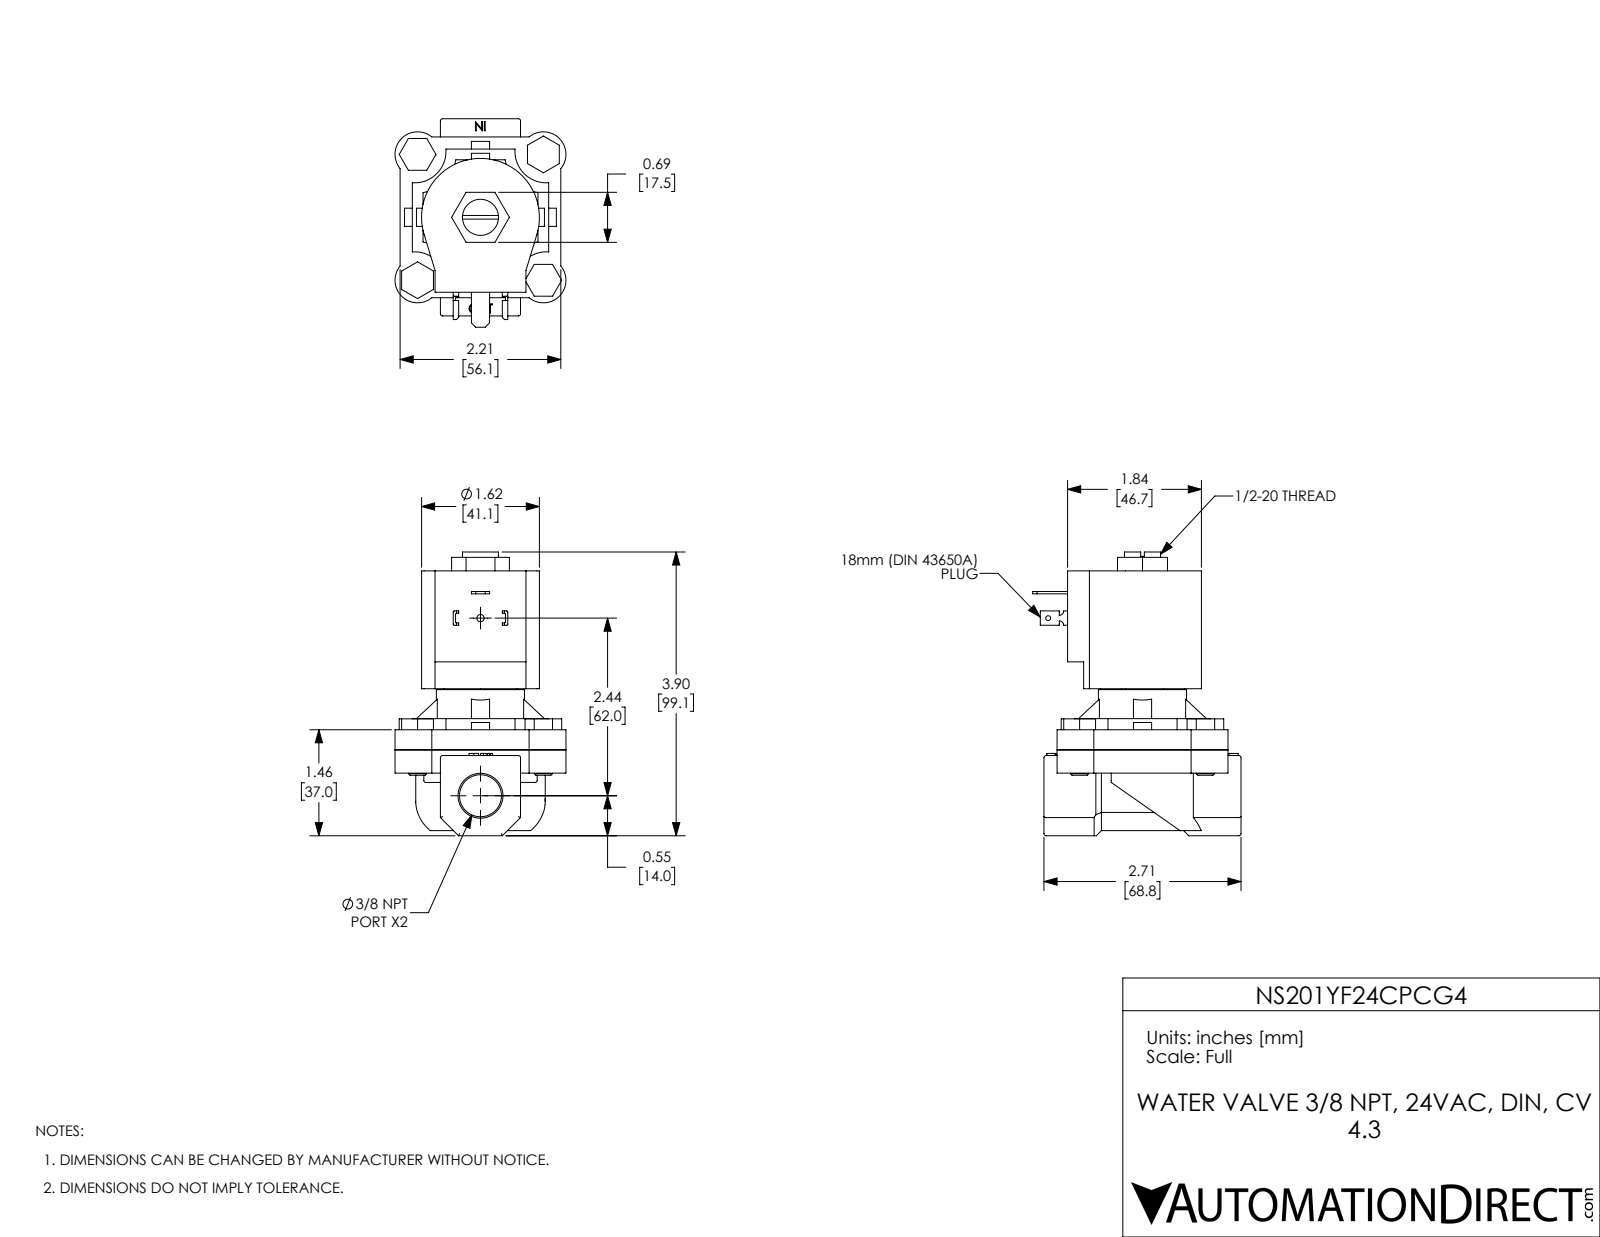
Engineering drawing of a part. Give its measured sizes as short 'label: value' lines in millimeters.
name: NS201YF24CPCG4
written by: SolidWorks 2021 (CONFIG_CONTROL_DESIGN)
unit: mm
bodies: 11 solids, 383 faces (237 planar, 113 cylindrical, 33 other)
size: 99.1 × 72.8 × 59.7
volume: 168 300 mm³; area: 42 940 mm²
holes: 4× ⌀6.4, 1× ⌀1.7, 1× ⌀2.5, 1× ⌀12.6, 1× ⌀13, 1× ⌀14.7, 1× ⌀29.3
bosses: 4× ⌀6.3, 1× ⌀30.8
rounds: 15× R0.8, 8× R0.4, 4× R7.9, 4× R11, 4× R14.7, 2× R1.5, 1× R20.6, 1× R22.6
face distances: 7, 62.5, 55.4, 8.1, 15.1, 70.6, 14.1, 42.1, 6.4, 28
hole spacings: 31.1, 43.9, 62.1, 62
